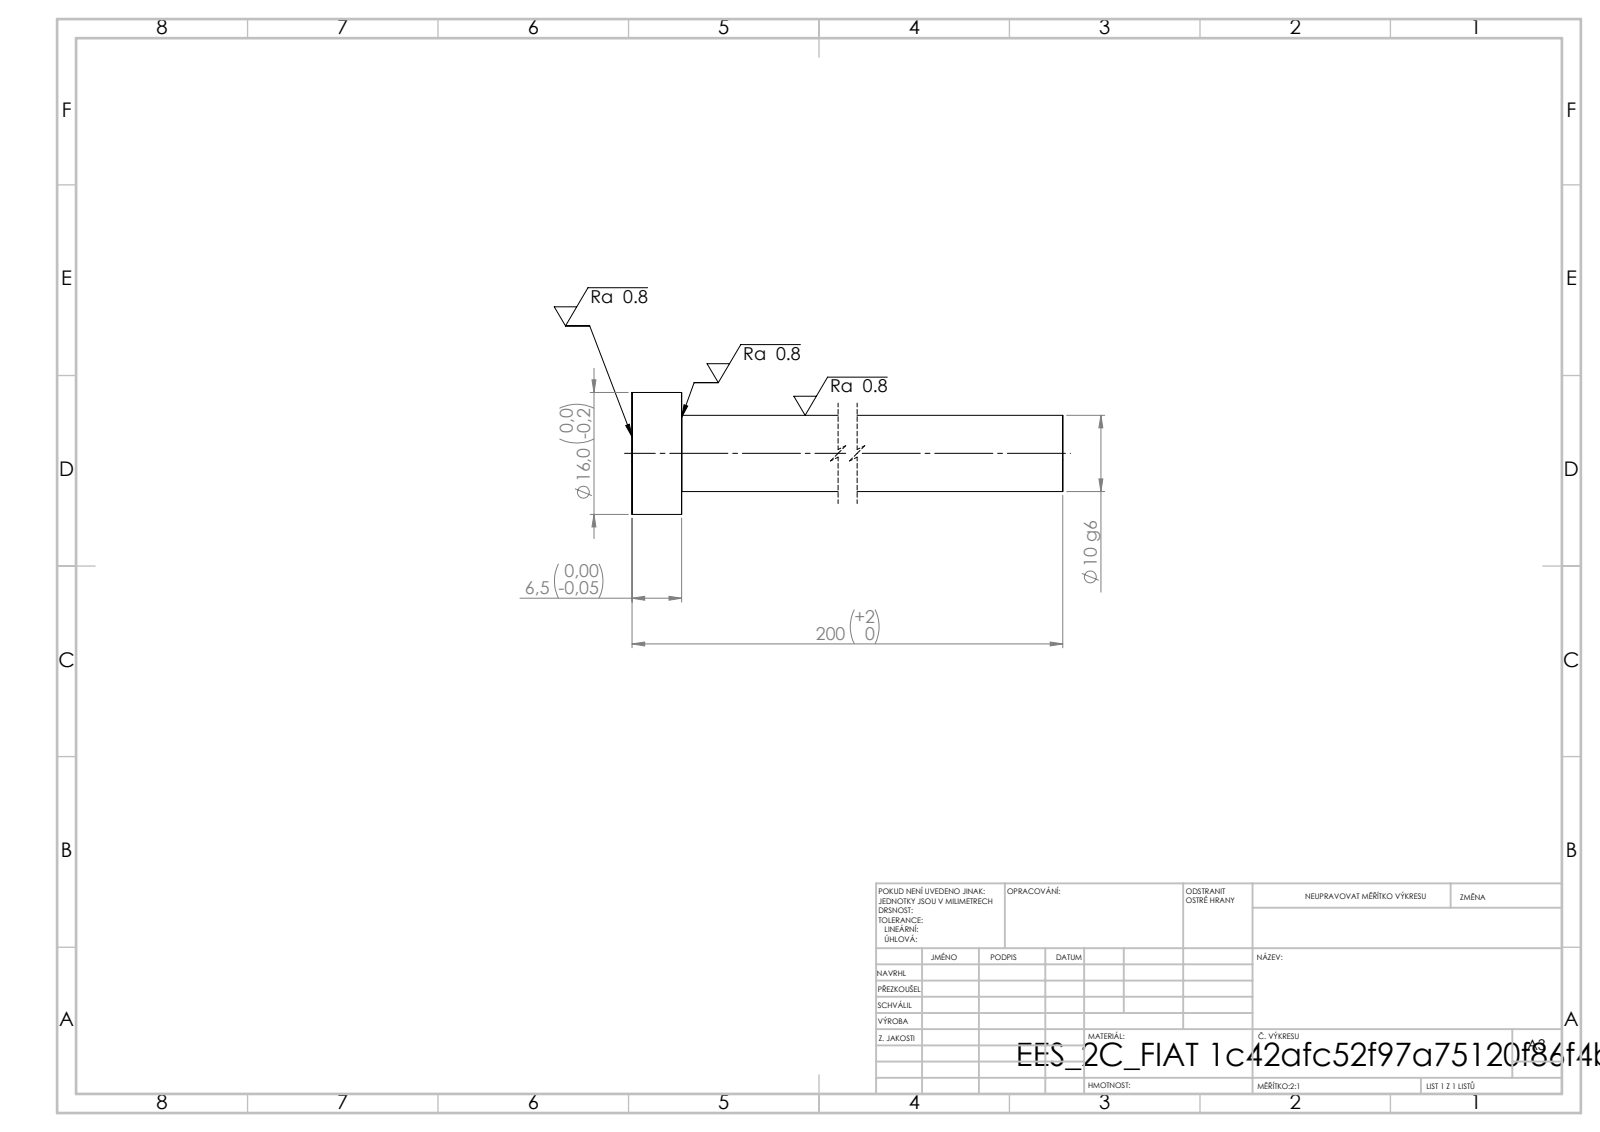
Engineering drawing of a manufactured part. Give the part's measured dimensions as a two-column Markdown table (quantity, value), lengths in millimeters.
| quantity | value |
| --- | --- |
| STEP written by | SolidWorks 2019 (CONFIG_CONTROL_DESIGN) |
| units | millimeters |
| bodies | 1 solid, 7 faces (3 planar, 4 cylindrical, 0 other) |
| overall size | 200 × 16 × 16 |
| volume | 16 504 mm³ |
| surface area | 6 808 mm² |
| round bosses / shafts (diameter × count) | 16 × 1, 10 × 1 |
| main face-to-face distances | 6.5, 200, 193.5 |
